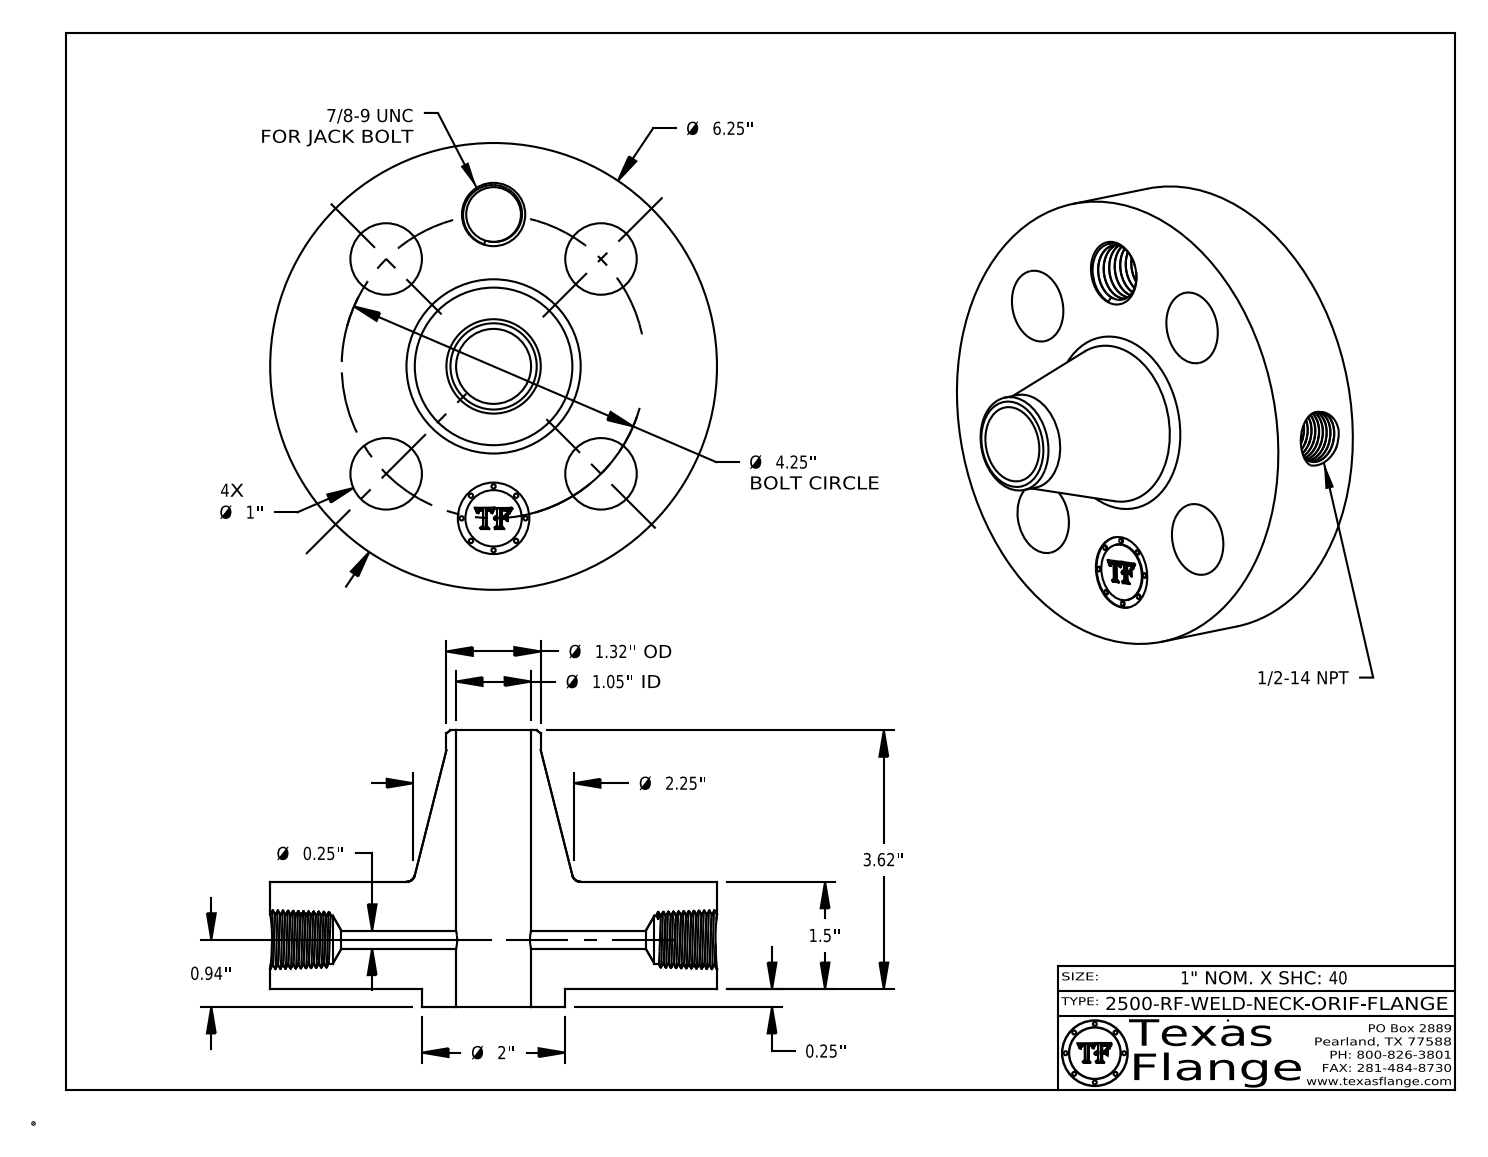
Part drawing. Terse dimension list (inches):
name: 2500-RF-WELD-NECK
written by: CATIA V5 STEP AP214 (AUTOMOTIVE_DESIGN)
unit: in
bodies: 1 solid, 751 faces (369 planar, 82 cylindrical, 300 other)
size: 6.25 × 6.25 × 3.87
volume: 42.11 in³; area: 138.7 in²
holes: 5× ⌀1, 1× ⌀0.25, 1× ⌀0.672, 1× ⌀0.766, 1× ⌀1.049
bosses: 8× ⌀0.061, 1× ⌀6.25, 1× ⌀2, 1× ⌀1.32, 1× ⌀0.788
face distances: 1.5, 0.25, 1.75, 0.015, 1.735, 1.485, 3.87, 3.62, 2.135, 2.12
hole spacings: 2.125, 1.626, 3.006, 3.927, 4.25
